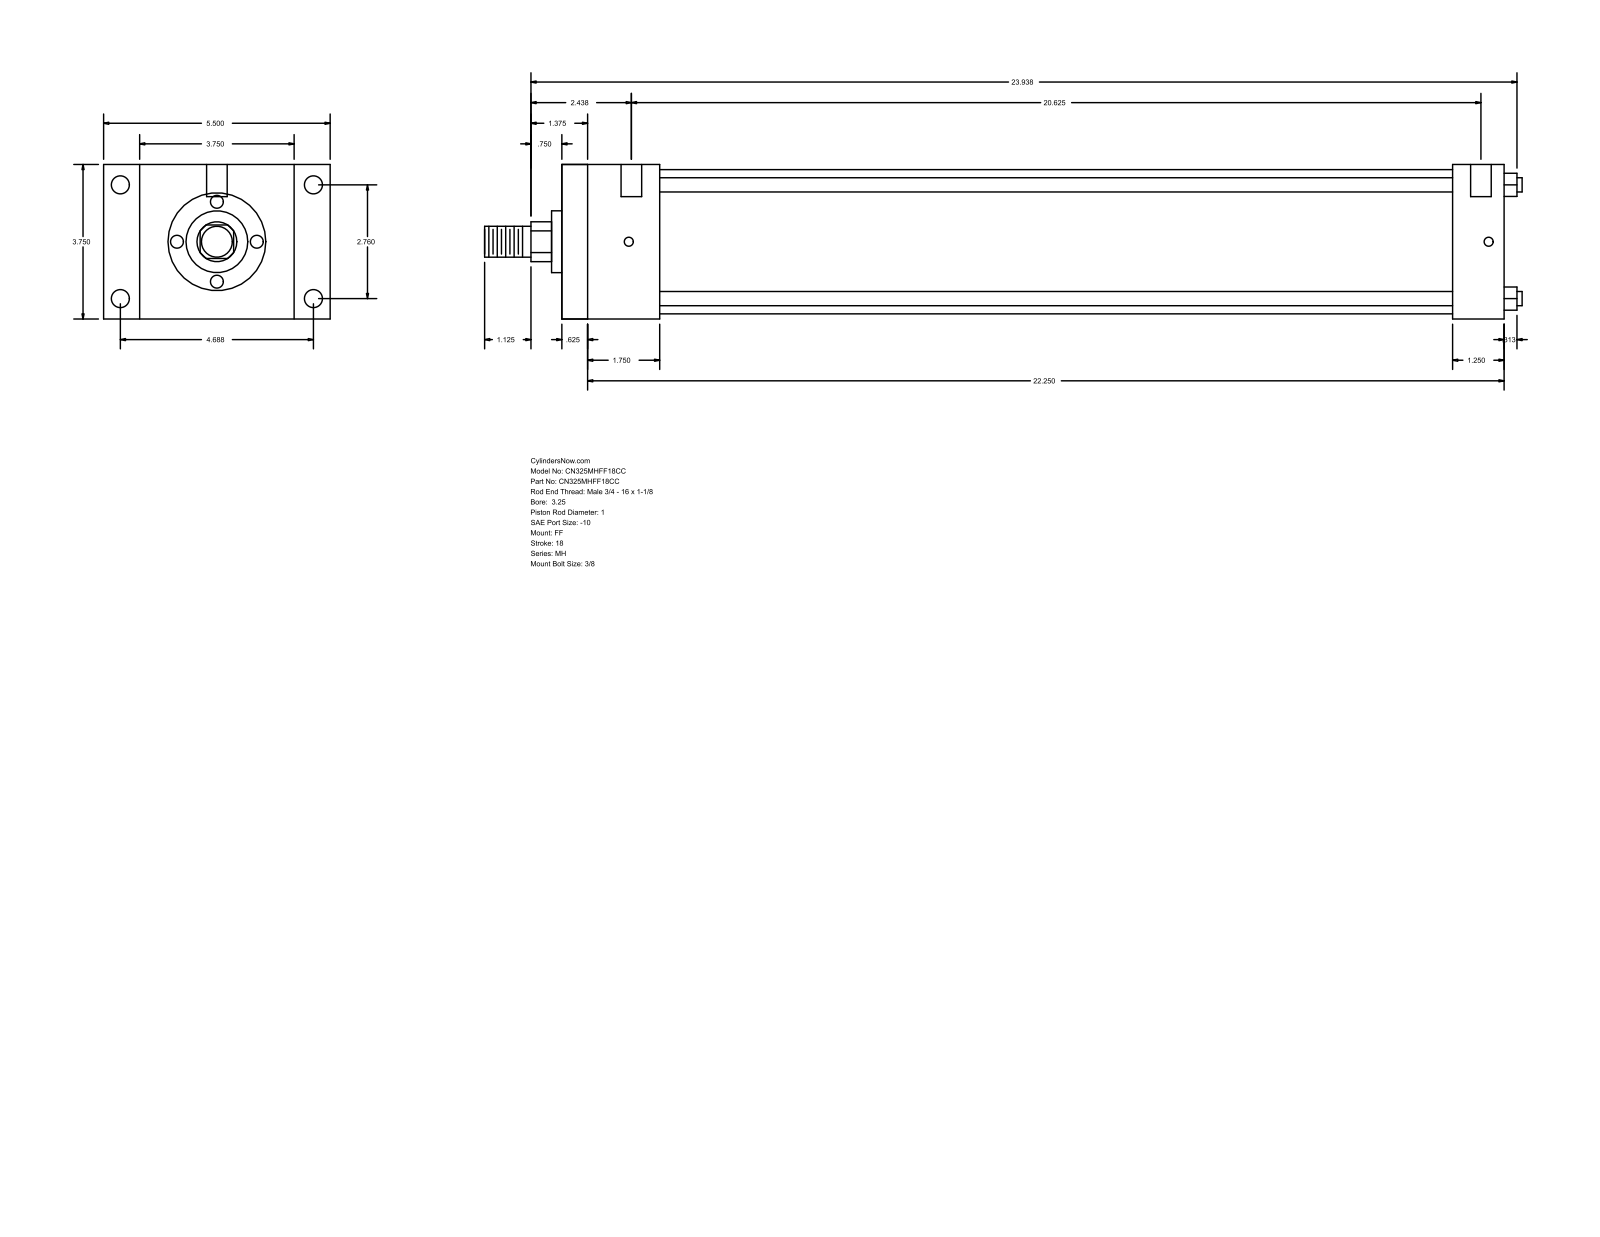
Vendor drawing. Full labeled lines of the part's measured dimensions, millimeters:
Part name (STEP PRODUCT): MH_FF__0325_1
STEP written by: GSSL Pune (CONFIG_CONTROL_DESIGN)
Units: millimetres
Bodies: 0 solids, 92 faces (64 planar, 28 cylindrical, 0 other)
Overall size (bounding box): 639.76 × 139.7 × 95.25
Round holes (diameter × count): ⌀5.56 ×4, ⌀11.13 ×4, ⌀12.7 ×2
Round bosses / shafts (diameter × count): ⌀8.76 ×4, ⌀88.9 ×1, ⌀38.1 ×1, ⌀25.4 ×1, ⌀19.05 ×1
Partial cylindrical surfaces — rounded edges, fillets, slot ends (radius × count): R12.29 ×1
Main face-to-face distances: 95.24, 581.03, 15.87, 565.16, 22.23, 117.47, 549.28, 533.41, 31.75, 60.33
Hole centre spacings: 70.1, 119.06, 138.16, 530.22, 1.58, 4.76, 523.88, 525.46
